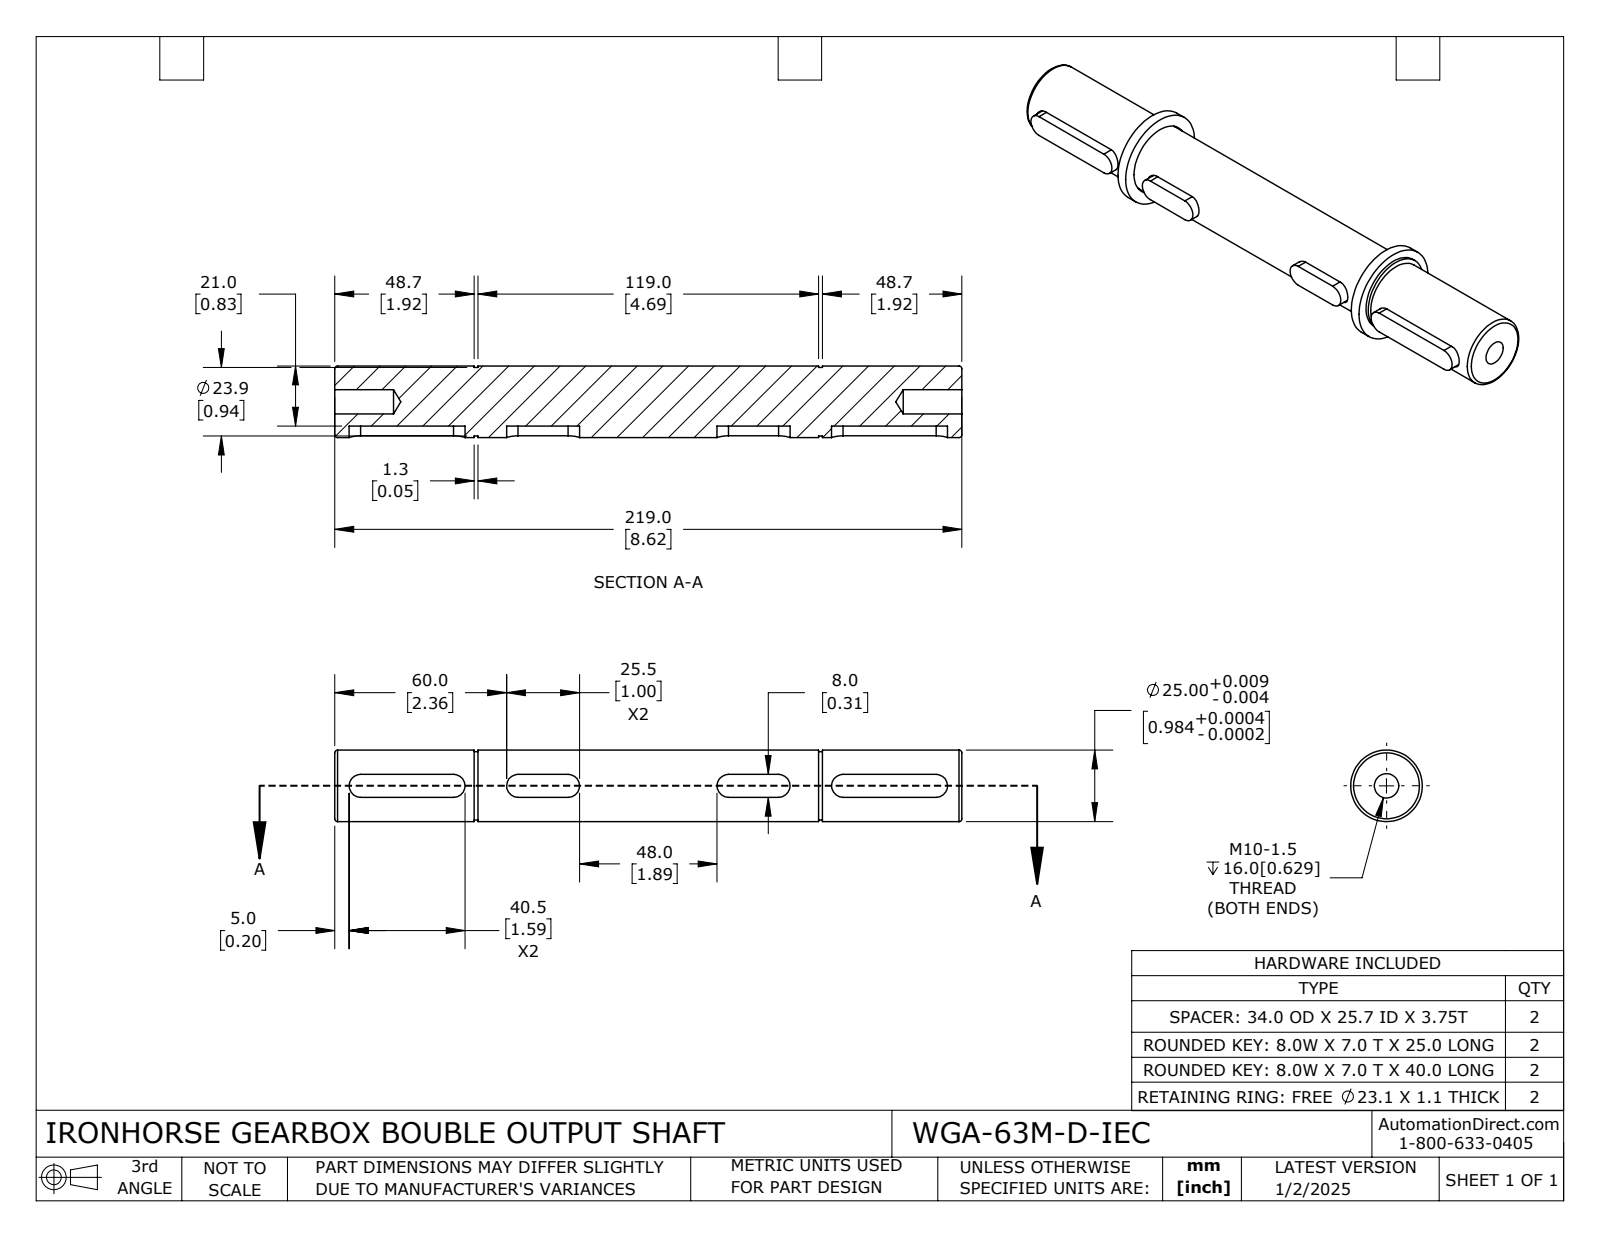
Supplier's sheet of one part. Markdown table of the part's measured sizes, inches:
| quantity | value |
| --- | --- |
| part name | WGA-63M-D-IEC |
| STEP written by | SolidWorks 2024 (CONFIG_CONTROL_DESIGN) |
| units | inches |
| bodies | 9 solids, 136 faces (54 planar, 74 cylindrical, 8 other) |
| overall size | 8.622 × 1.339 × 1.339 |
| volume | 6.796 in³ |
| surface area | 44.28 in² |
| round holes (diameter × count) | 0.075 × 2, 0.335 × 1, 0.89 × 1, 1.012 × 1 |
| round bosses / shafts (diameter × count) | 1.339 × 1, 1.065 × 1, 0.984 × 1, 0.941 × 1 |
| partial cylindrical surfaces (radius × count) | 0.157 × 12, 0.02 × 2, 0.102 × 2 |
| main face-to-face distances | 0.315, 0.276, 0.148, 4.537, 1.969, 2.116, 6.506, 6.654, 4.685, 4.39 |
| hole center spacings | 0.541, 0.118 |
